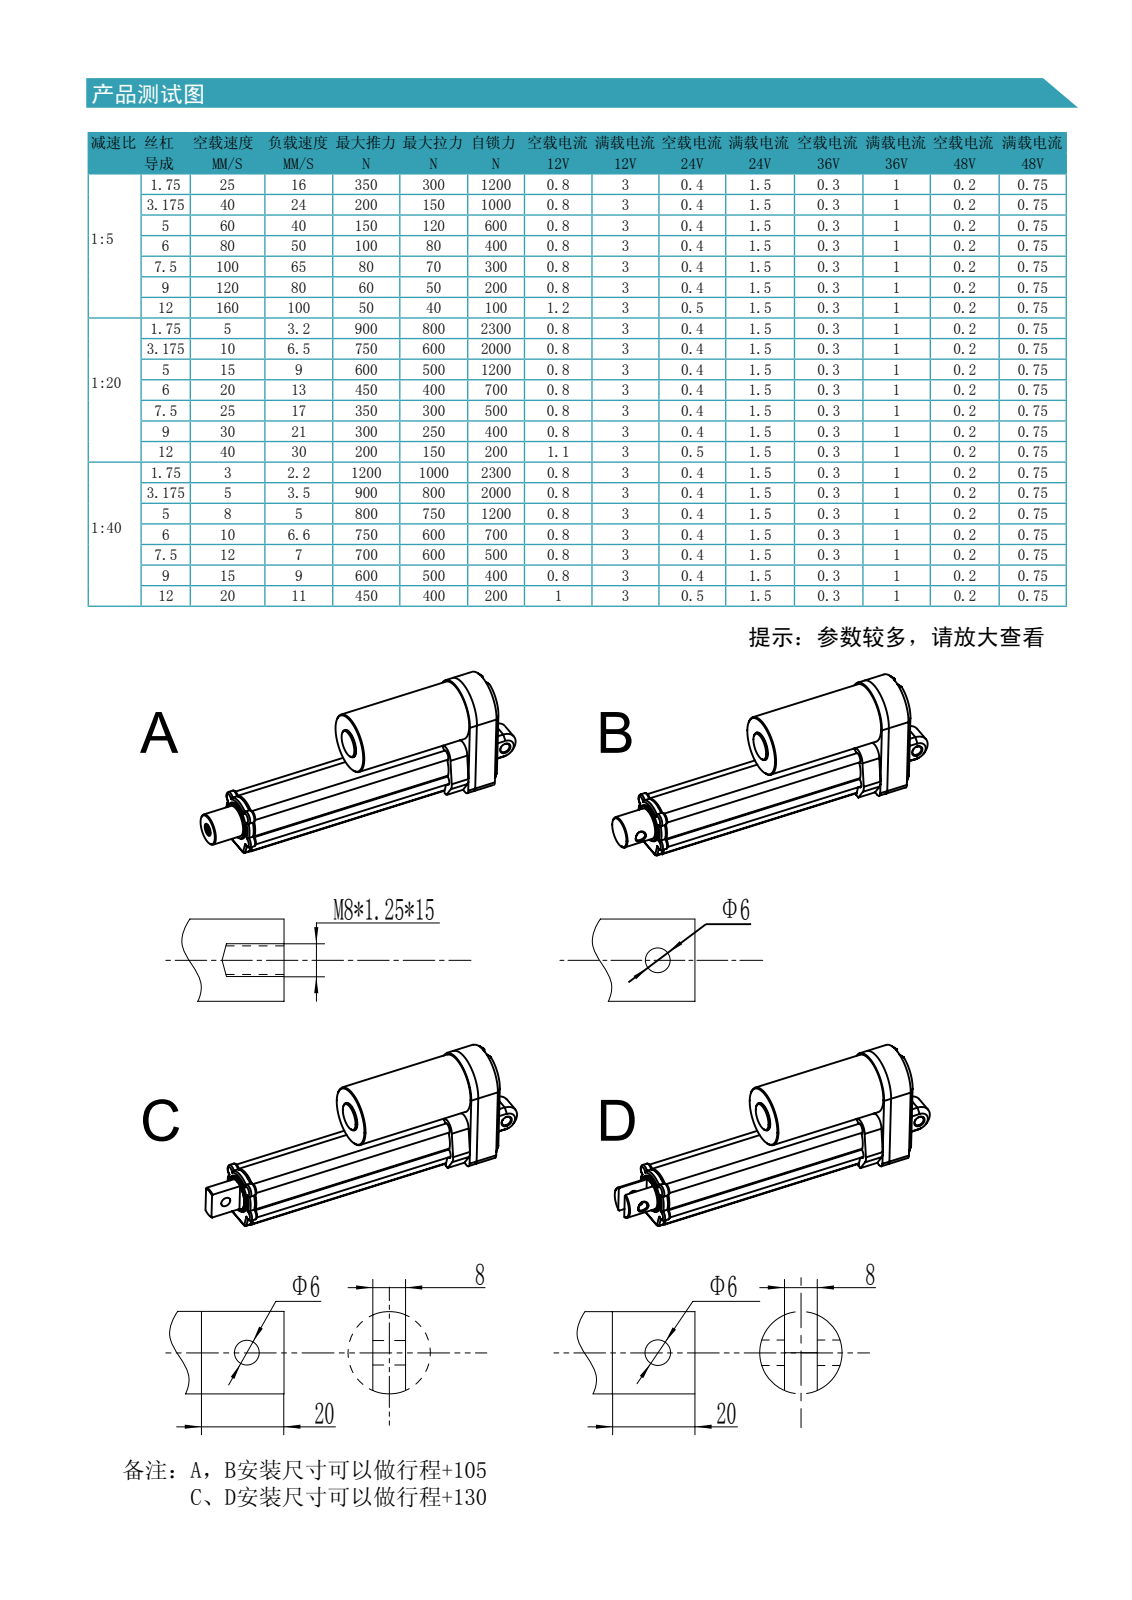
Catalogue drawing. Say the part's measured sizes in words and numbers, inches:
The part is named "TGA-E-BOTTOM; HF-TGA-E-UP; HF-TGA-EWAIKE; MOTOR (+3 more)". Its 3-D file was written by "PRO/ENGINEER BY PARAMETRIC TECHNOLOGY CORPORATION, 2008380 (CONFIG_CONTROL_DESIGN)". It is 6 solids with 206 faces: 75 planar, 80 cylindrical and 51 other. Overall it measures 223.994 by 74.501 by 40.144 inches. Its volume is 241 753 cubic inches and its surface area 82 986 square inches. Round holes: 4 of diameter 3, 2 of diameter 6.4, 1 of diameter 20. Round bosses or shafts: 1 of diameter 38, 1 of diameter 25.4, 1 of diameter 23, 1 of diameter 18. Partial cylindrical surfaces (rounded edges, fillets, slot ends): 8 of radius 2, 7 of radius 4, 6 of radius 1, 4 of radius 3, 4 of radius 3.5, 3 of radius 4.002, 2 of radius 0.5, 2 of radius 1.668. The main face-to-face distances are 5, 1.801, 17, 22, 1.806, 1.796, 40, 156.707, 97.5, 80.5. The hole center spacings are 15.521, 18.123, 14.899, 14.899, 22.269, 26.48, 30.3, 30.3.
